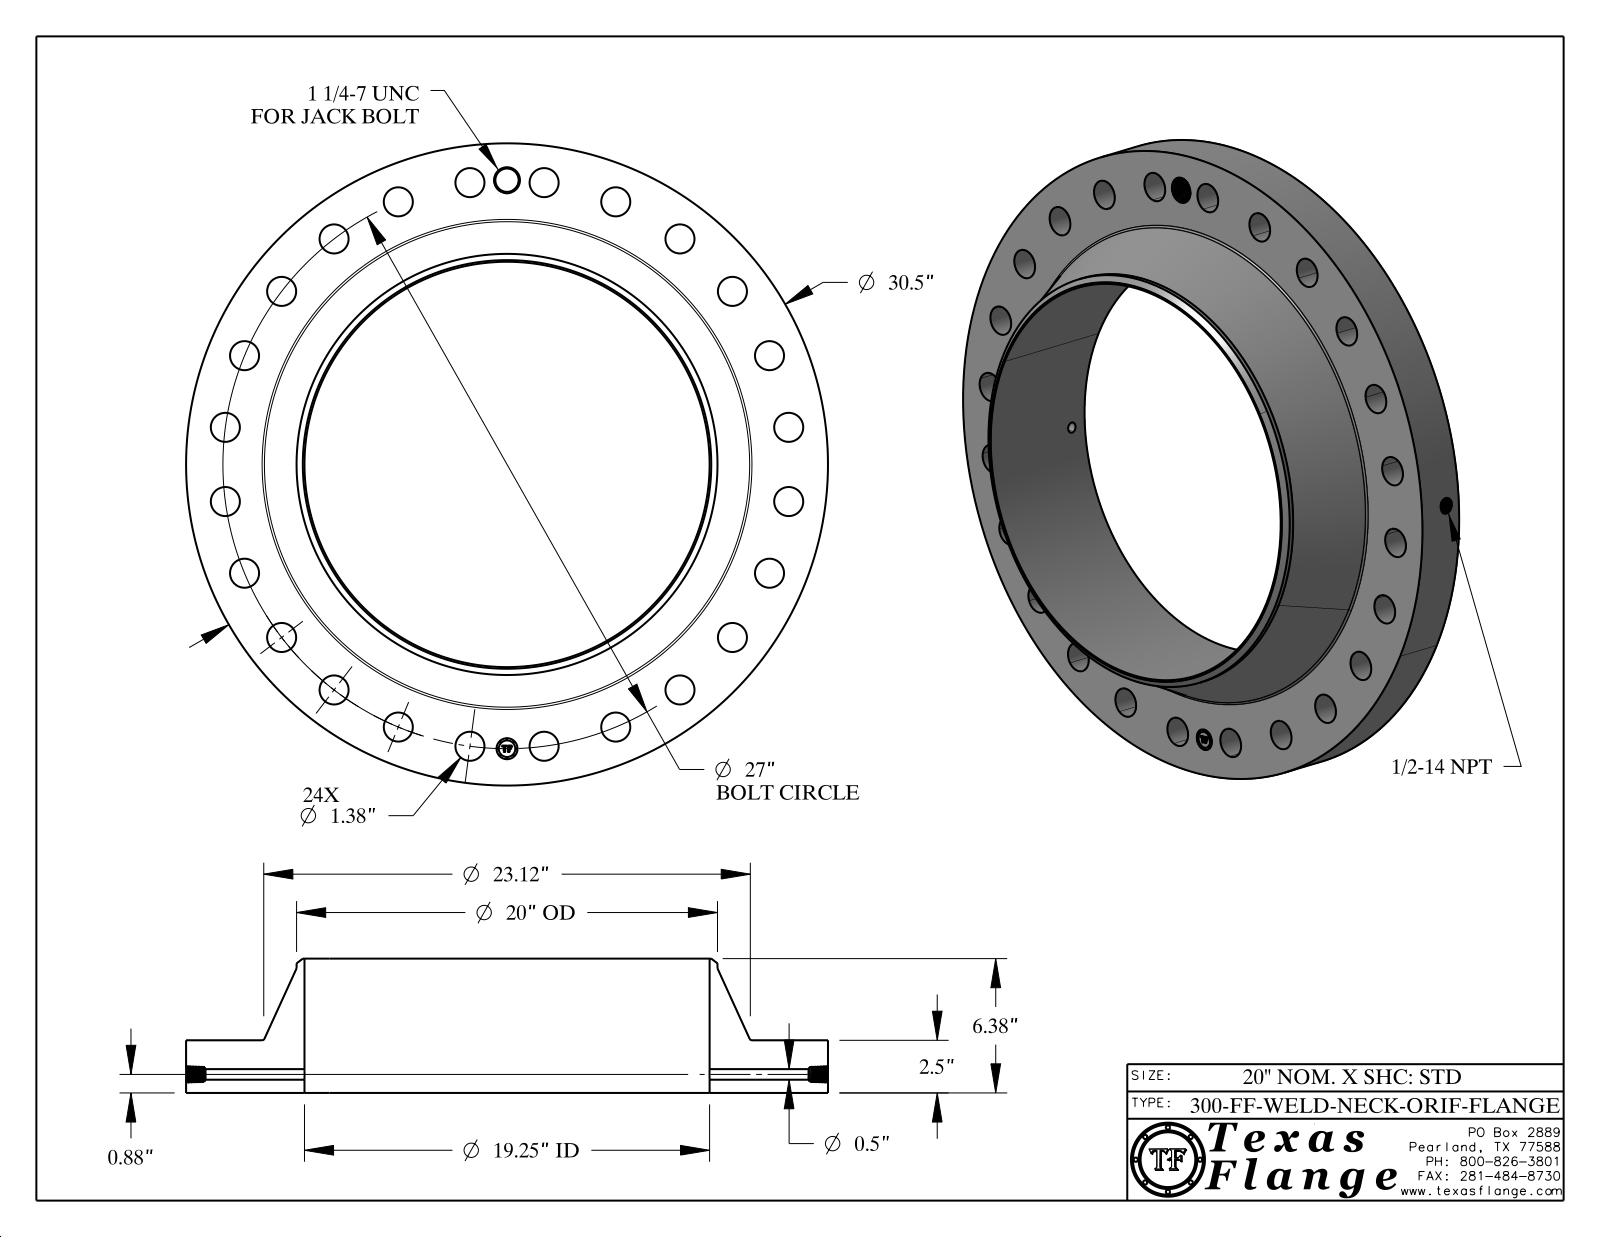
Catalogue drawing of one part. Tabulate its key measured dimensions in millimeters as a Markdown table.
| quantity | value |
| --- | --- |
| part name | 300-FF-WELD-NECK |
| STEP written by | CATIA V5 STEP AP214 (AUTOMOTIVE_DESIGN) |
| units | millimeters |
| bodies | 1 solid, 815 faces (368 planar, 129 cylindrical, 318 other) |
| overall size | 774.7 × 774.7 × 162.1 |
| volume | 20 780 000 mm³ |
| surface area | 1 221 000 mm² |
| round holes (diameter × count) | 35.1 × 24, 12.7 × 1, 17.1 × 1, 25.4 × 1, 28.2 × 1, 489 × 1 |
| round bosses / shafts (diameter × count) | 1.5 × 8, 774.7 × 1, 508 × 1, 20 × 1 |
| main face-to-face distances | 63.5, 162.1, 98.6, 63.1, 0.4, 98.9, 7.6, 7.4, 1.4, 6.3 |
| hole center spacings | 342.9, 593.9, 633.6, 544.1, 89.5, 177.5, 484.9, 662.4 |
